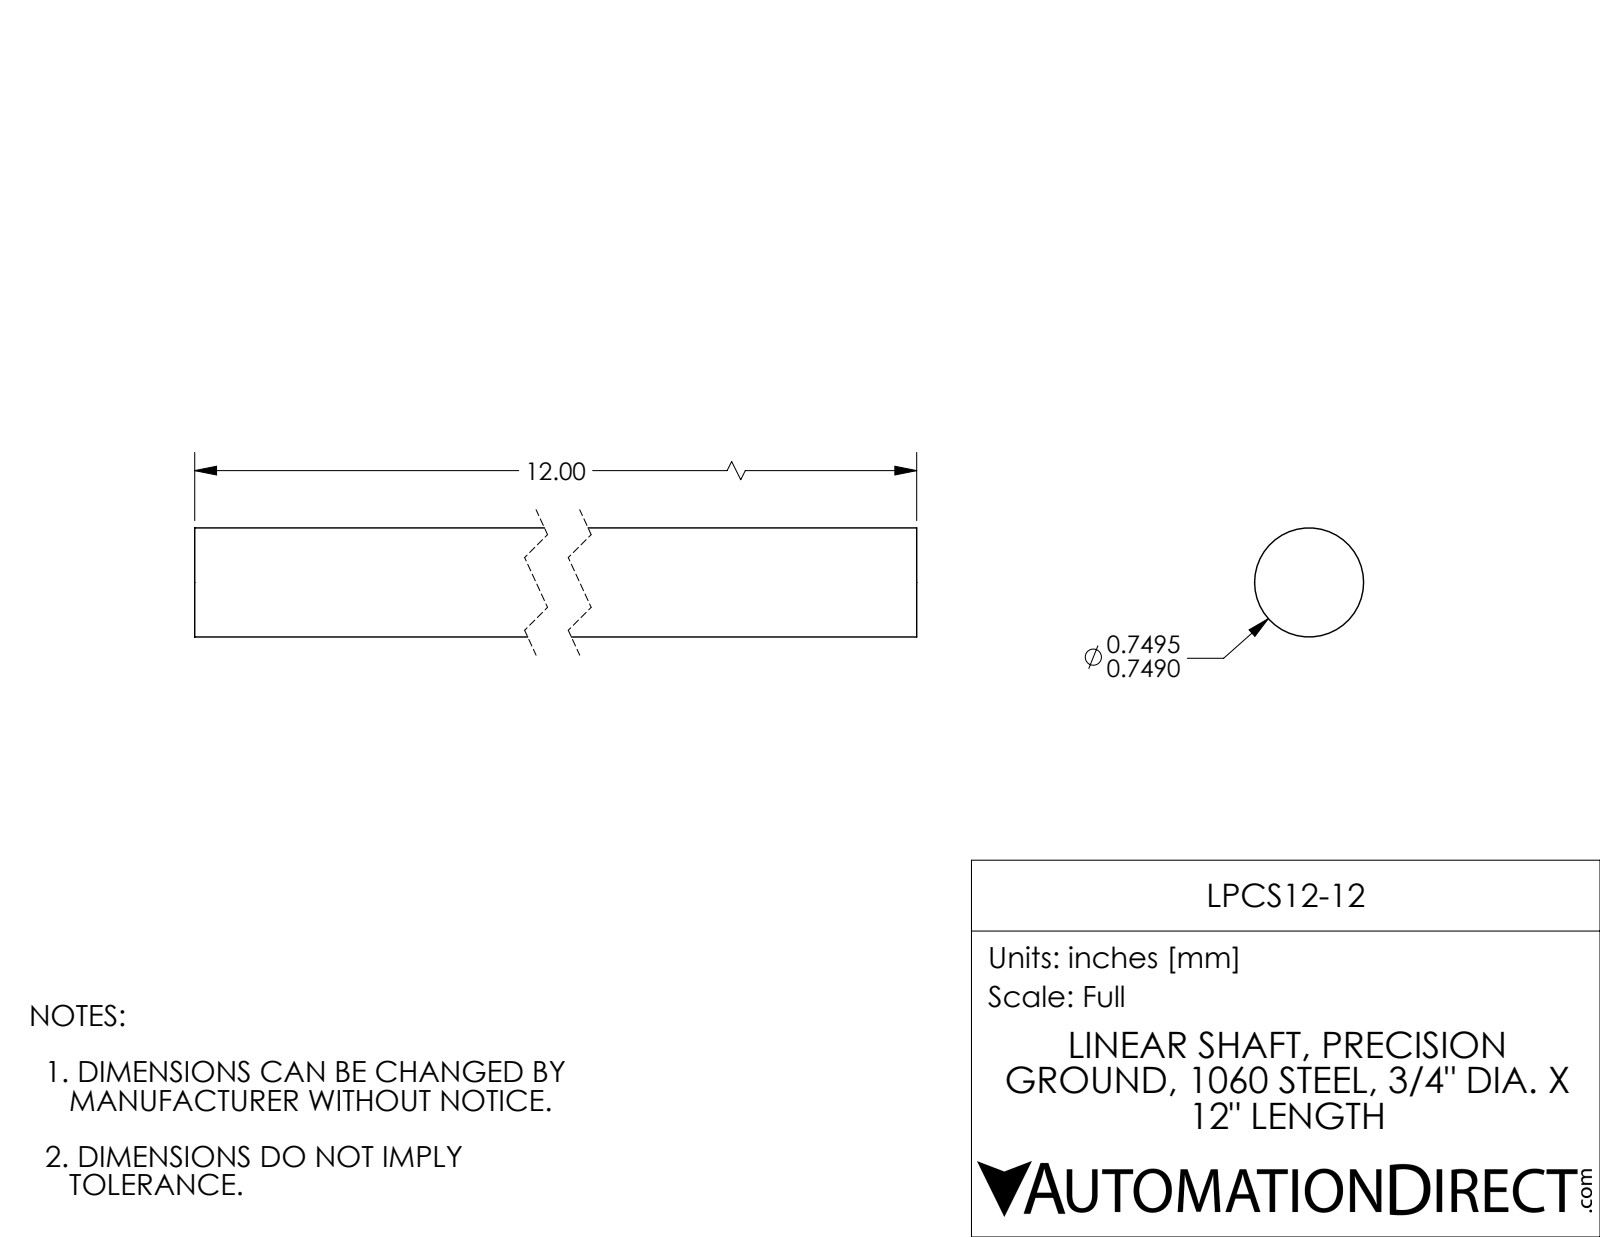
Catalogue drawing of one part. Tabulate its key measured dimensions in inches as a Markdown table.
| quantity | value |
| --- | --- |
| part name | LPCS12-12 |
| STEP written by | SolidWorks 2017 (AUTOMOTIVE_DESIGN) |
| units | inches |
| bodies | 1 solid, 4 faces (2 planar, 2 cylindrical, 0 other) |
| overall size | 12 × 0.749 × 0.749 |
| volume | 5.294 in³ |
| surface area | 29.14 in² |
| round bosses / shafts (diameter × count) | 0.75 × 1 |
| main face-to-face distances | 12 |
